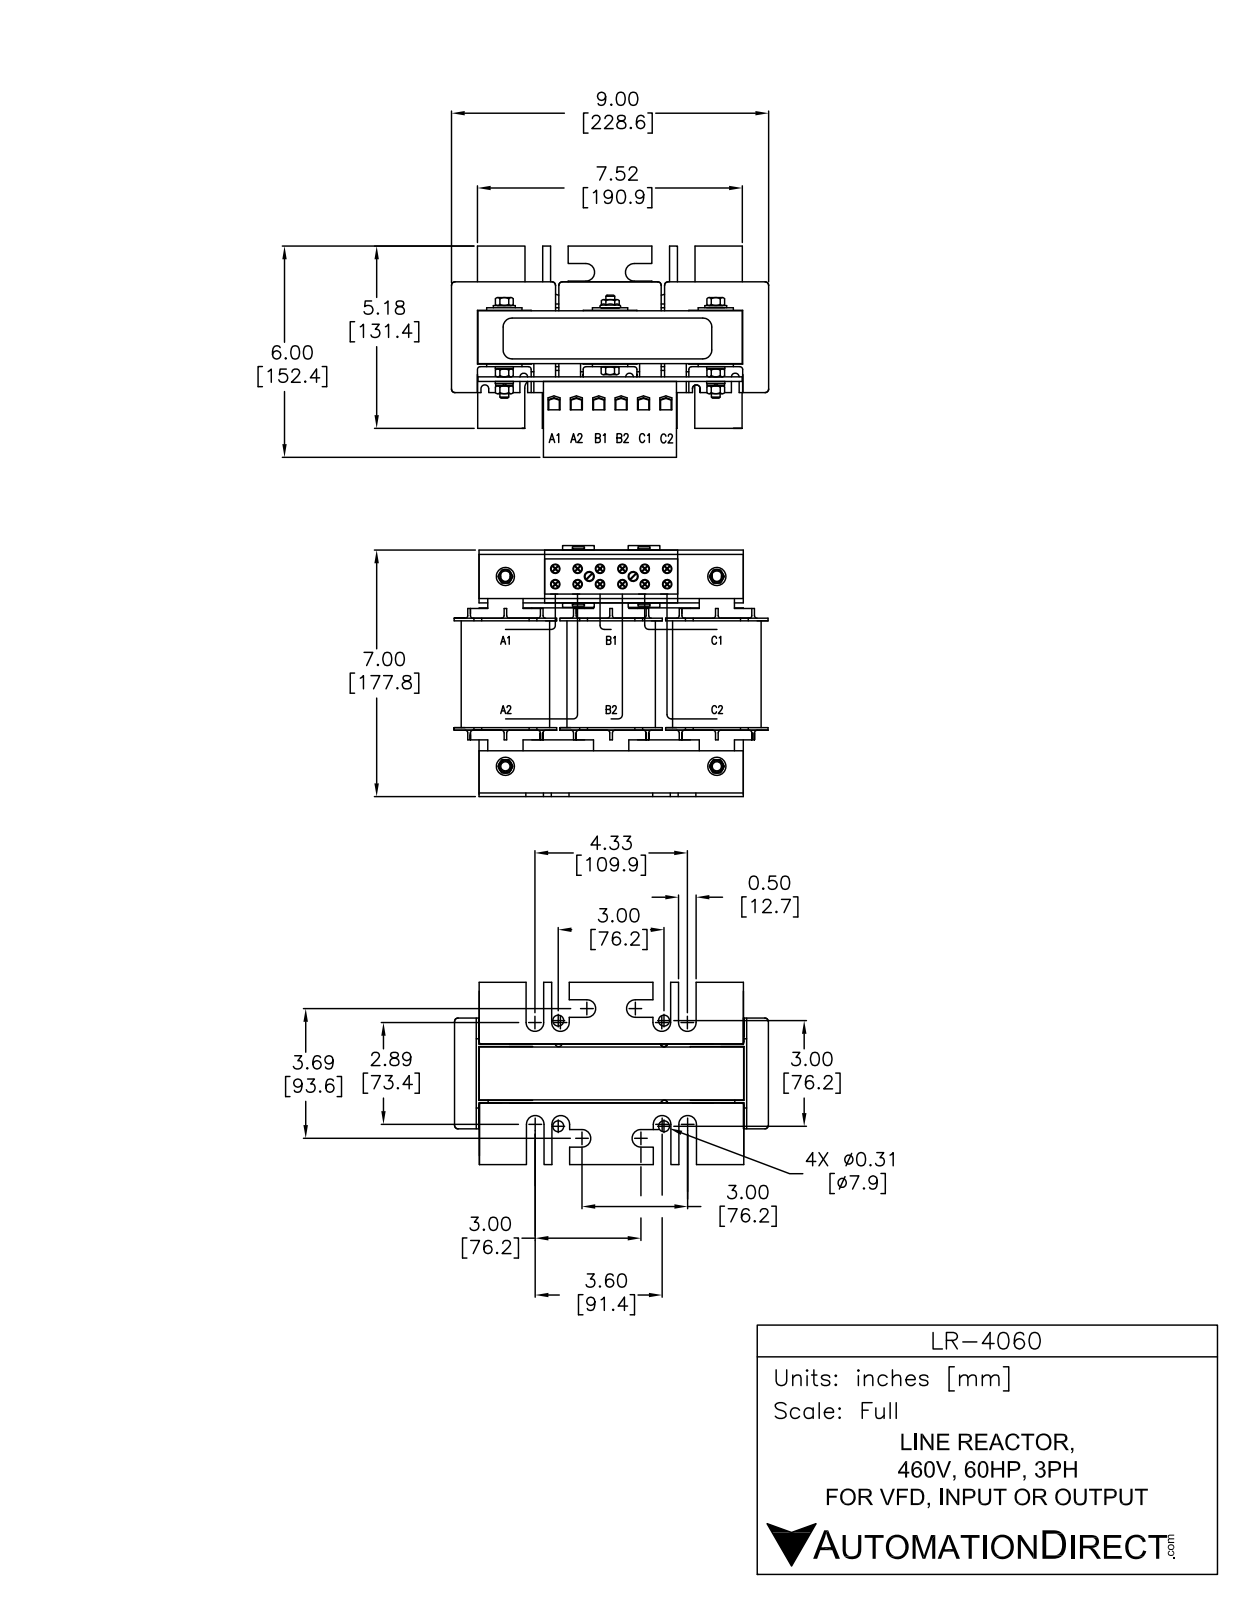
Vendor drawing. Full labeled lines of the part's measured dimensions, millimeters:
Part name (STEP PRODUCT): LR-4060
STEP written by: SolidWorks 2011 (AUTOMOTIVE_DESIGN)
Units: millimetres
Bodies: 48 solids, 1510 faces (855 planar, 512 cylindrical, 143 other)
Overall size (bounding box): 227 × 177.7 × 136.42
Volume: 2 658 000 mm³ · Surface area: 472 550 mm²
Round holes (diameter × count): ⌀6.8 ×12, ⌀8.62 ×12, ⌀7.25 ×5
Round bosses / shafts (diameter × count): ⌀10.25 ×12, ⌀6.8 ×9, ⌀15 ×5, ⌀18.75 ×3, ⌀6 ×3, ⌀6 ×2
Partial cylindrical surfaces — rounded edges, fillets, slot ends (radius × count): R0.75 ×130, R1 ×12, R6.35 ×12, R7 ×12, R15 ×12, R3.4 ×11, R2.75 ×8, R4.71 ×5
Main face-to-face distances: 76.5, 2, 78.5, 7, 42.5, 38, 38.5, 9.75, 9, 85.5
Hole centre spacings: 16, 32, 40.84, 48, 22.45, 15.69, 15.75, 22.41
